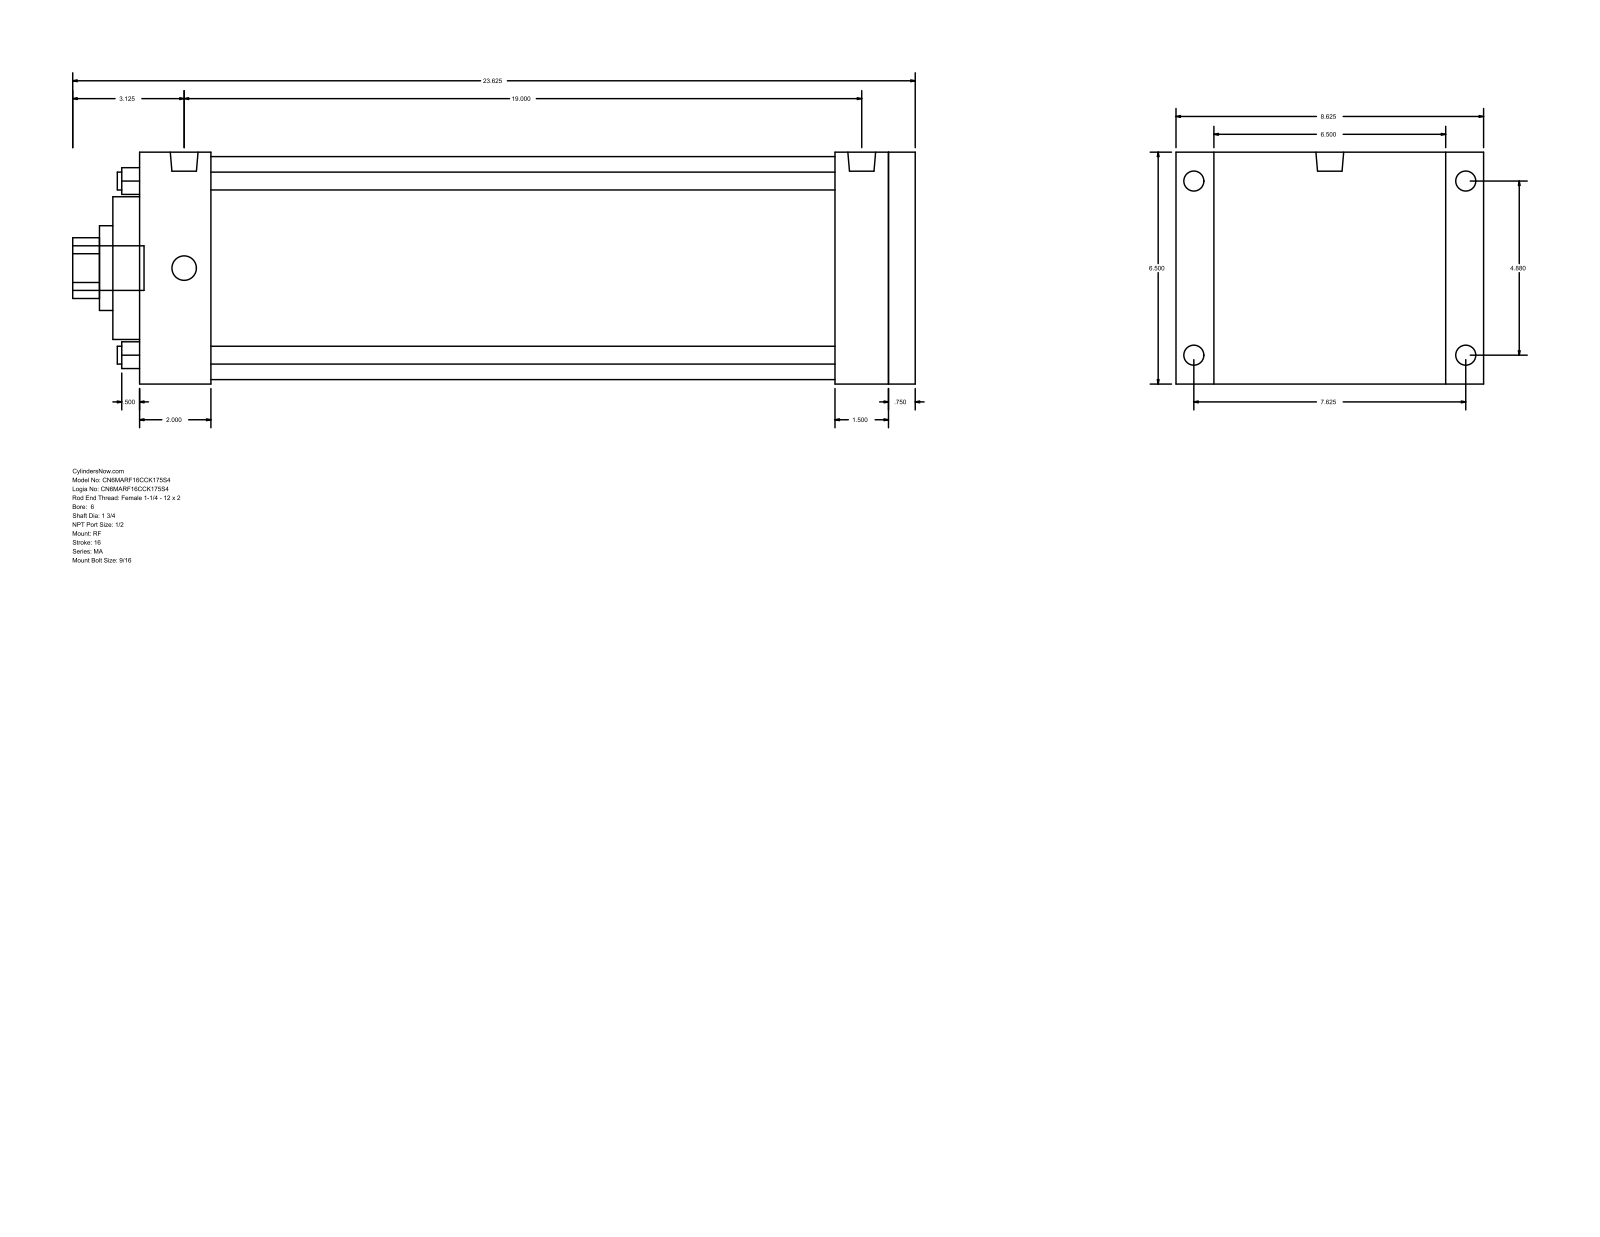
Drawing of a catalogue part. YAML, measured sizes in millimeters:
part_name: "MA_RF__0600_1.75"
step_written_by: "GSSL Pune (CONFIG_CONTROL_DESIGN)"
units: millimeters
bodies: {solids: 0, faces: 94, planar: 65, cylindrical: 29, other: 0}
overall_size: [600.08, 219.07, 165.1]
round_holes:
  - {diameter: 12.7, count: 4}
  - {diameter: 44.45, count: 1}
  - {diameter: 60.33, count: 1}
  - {diameter: 101.6, count: 1}
  - {diameter: 158.75, count: 1}
round_bosses_or_shafts:
  - {diameter: 17.46, count: 4}
  - {diameter: 14.29, count: 4}
  - {diameter: 19.77, count: 2}
  - {diameter: 31.75, count: 1}
partial_cylinders:
  - {radius: 21.63, count: 1}
face_to_face_distances: [165.1, 552.46, 533.4, 19.06, 19.05, 38.1, 50.8, 482.6, 501.66, 495.3]
hole_center_spacings: [87.65, 123.96, 175.31]
